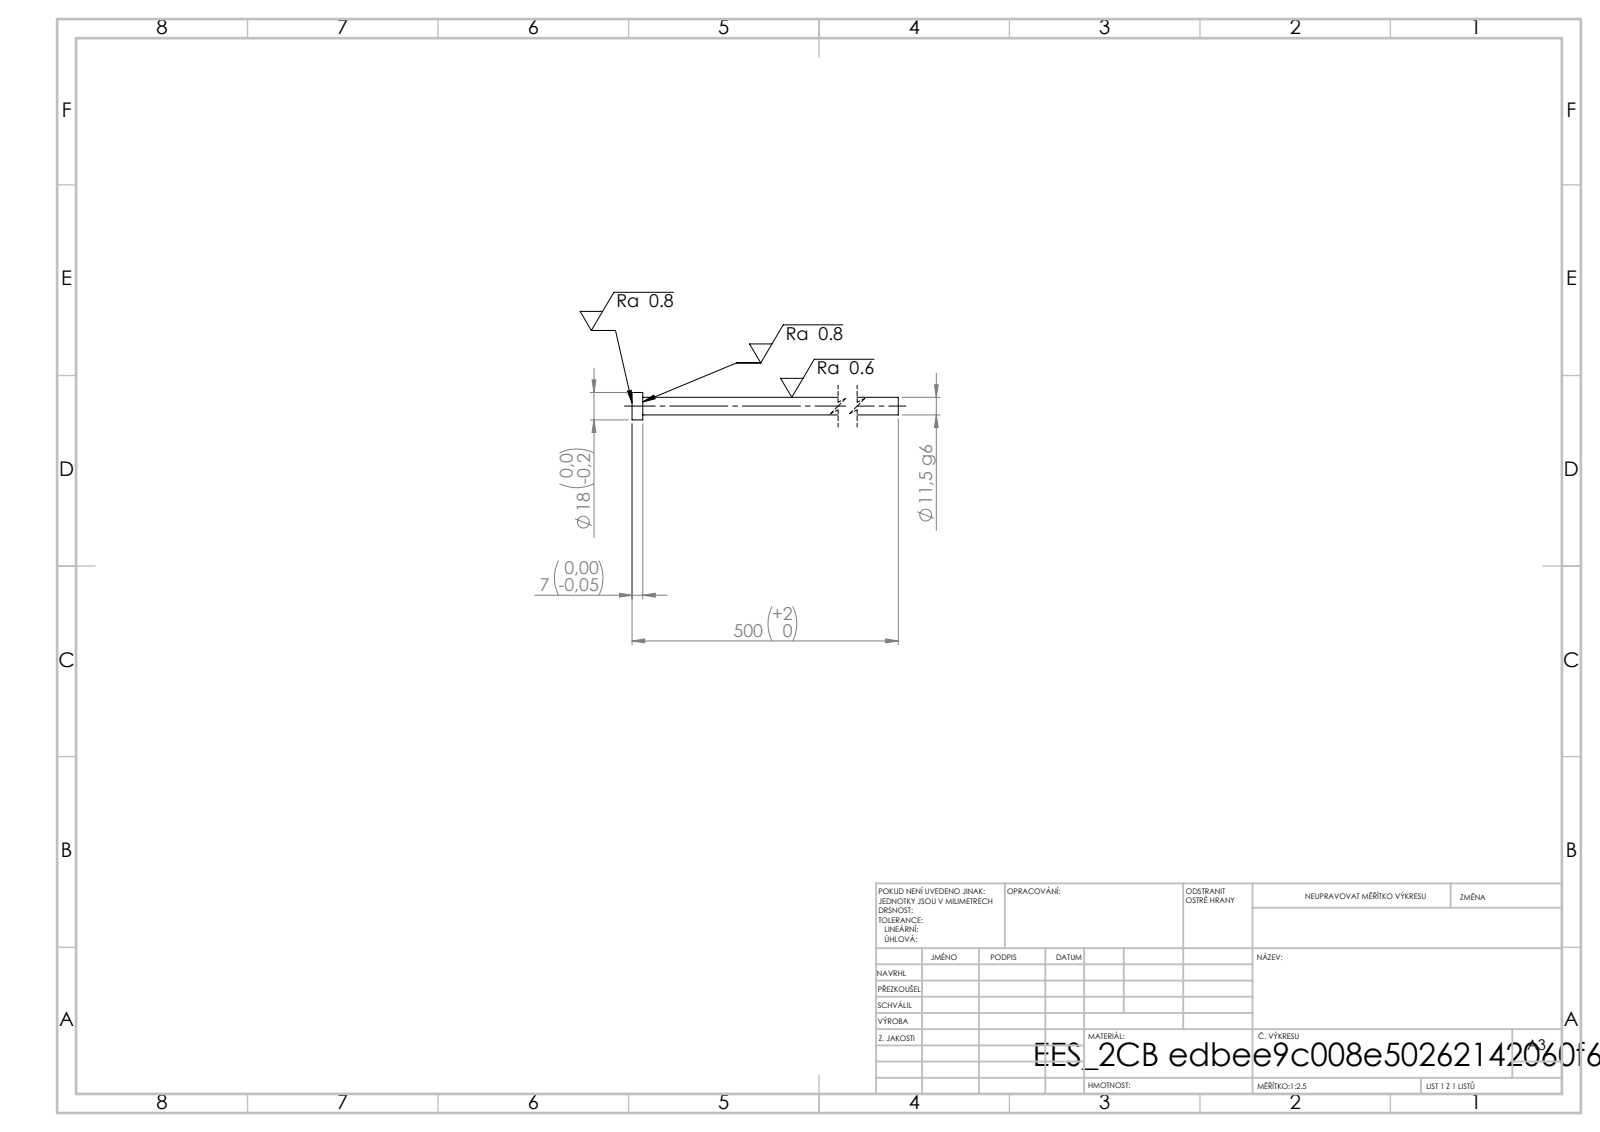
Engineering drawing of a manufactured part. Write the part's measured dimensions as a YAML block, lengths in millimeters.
step_written_by: "SolidWorks 2019 (CONFIG_CONTROL_DESIGN)"
units: millimeters
bodies: {solids: 1, faces: 7, planar: 3, cylindrical: 4, other: 0}
overall_size: [500, 18, 18]
volume: 52989
surface_area: 18716
round_bosses_or_shafts:
  - {diameter: 18, count: 1}
  - {diameter: 11.5, count: 1}
face_to_face_distances: [7, 500, 493]
